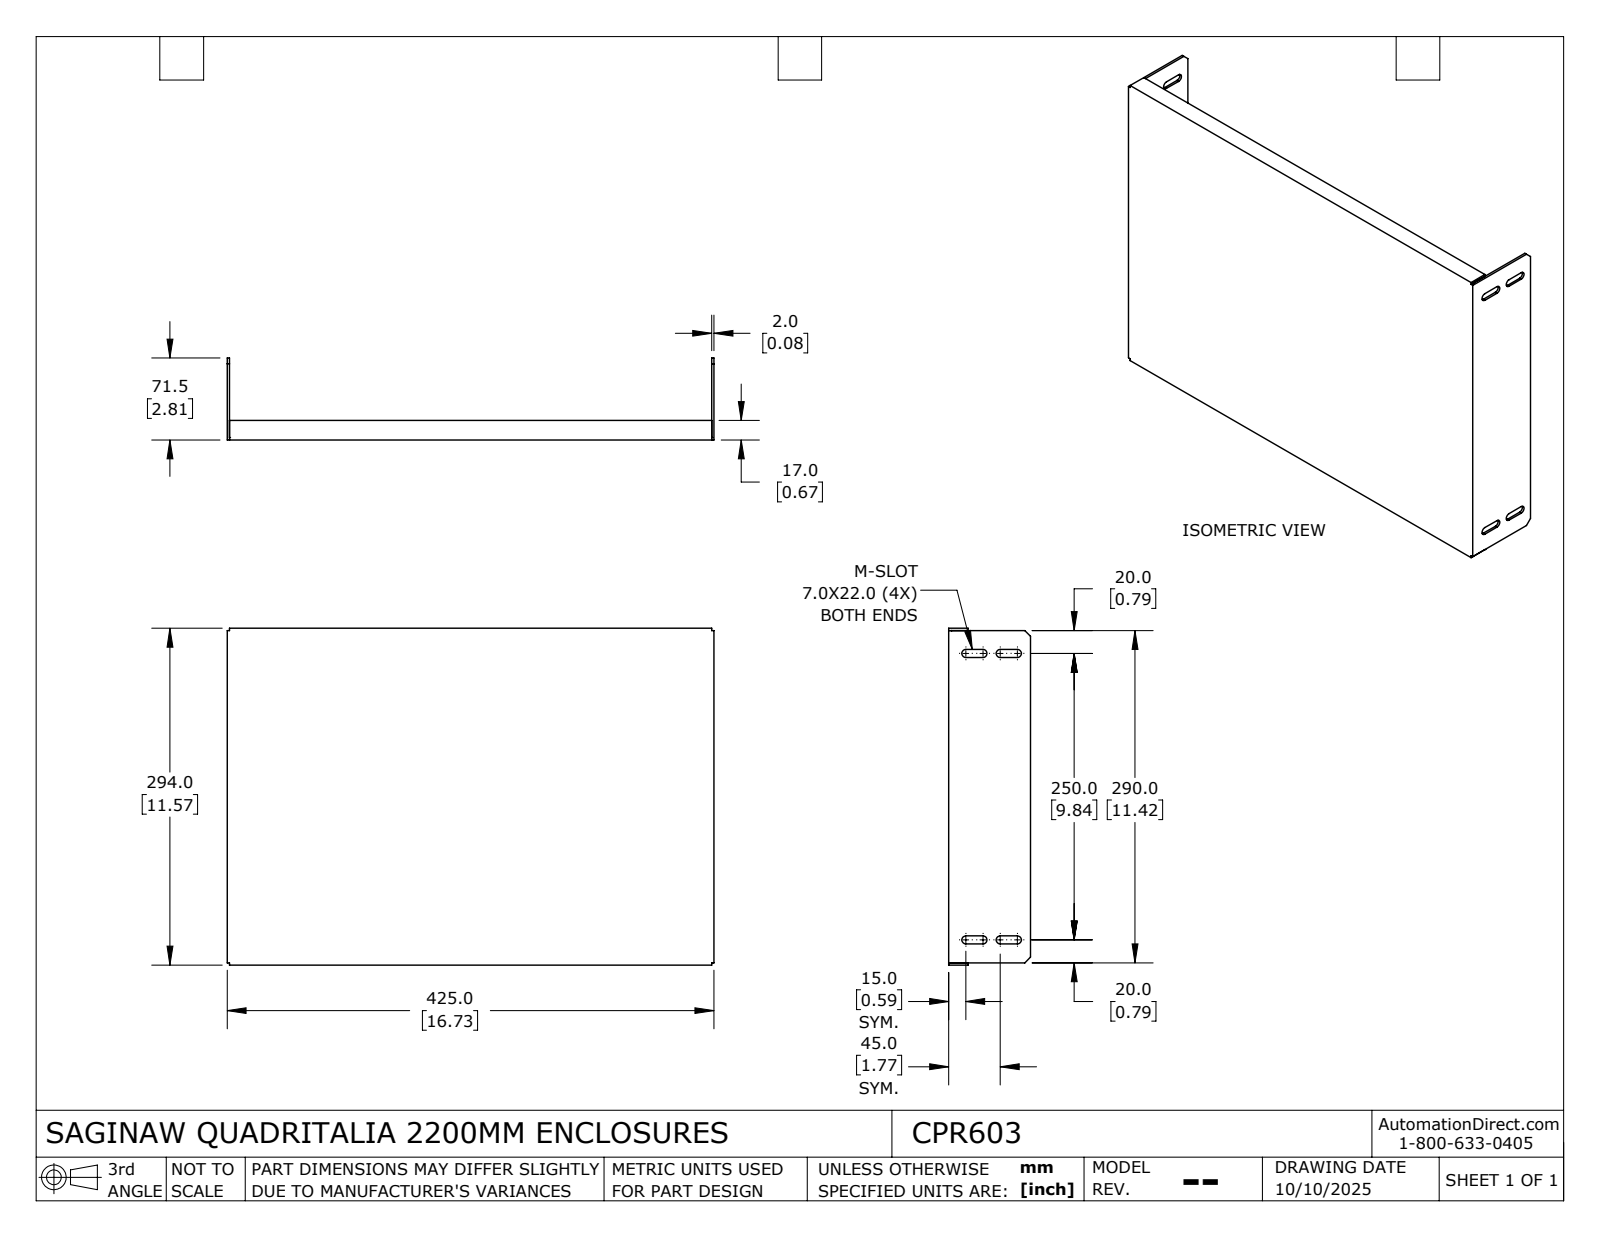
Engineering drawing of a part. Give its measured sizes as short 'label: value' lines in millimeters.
name: CPR603_Default
written by: SolidWorks 2024 (CONFIG_CONTROL_DESIGN)
unit: mm
bodies: 1 solid, 59 faces (43 planar, 16 cylindrical, 0 other)
size: 425 × 294 × 71.5
volume: 353 351 mm³; area: 357 711 mm²
rounds: 8× R3.5
face distances: 2, 423, 425, 421, 292, 294, 290, 17, 15, 71.5
